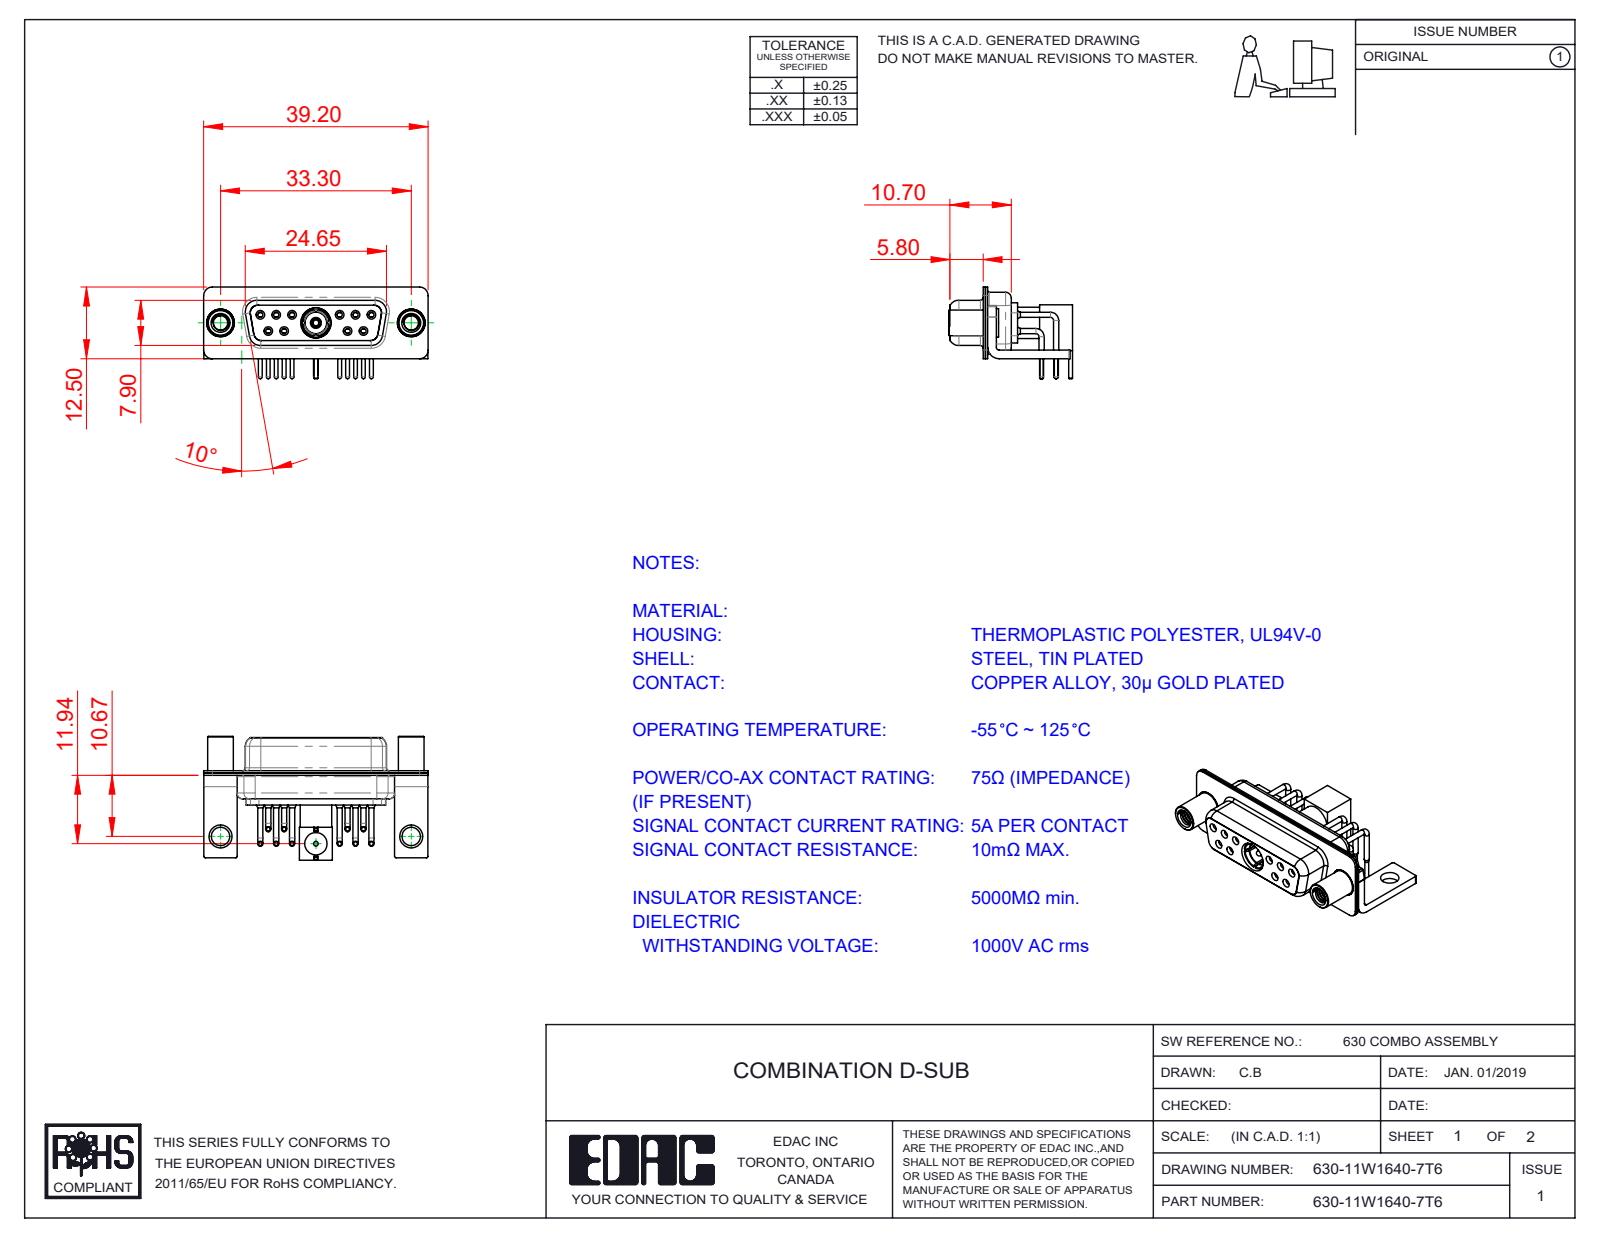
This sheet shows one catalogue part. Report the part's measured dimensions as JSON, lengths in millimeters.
{"part_name": "Co-Ax Plug_RA PC Tail; Locking Collar; 630Combo Shell Rear_15 Contacts; RA Back Shell (+8 more)", "step_written_by": "SolidWorks 2020 (CONFIG_CONTROL_DESIGN)", "units": "millimeters", "bodies": {"solids": 23, "faces": 1075, "planar": 306, "cylindrical": 504, "other": 265}, "overall_size": [39.2, 21.61, 16], "volume_mm3": 3196, "surface_area_mm2": 7818, "round_holes": [[1.1, 11], [1.5, 11], [0.9, 10], [2, 10], [1.7, 6], [1.6, 4], [4.85, 3], [2.5, 2], [3.2, 2], [4, 2], [4.05, 2], [0.8, 1]], "round_bosses_or_shafts": [[0.9, 10], [0.65, 10], [1.6, 6], [5, 3], [4.95, 2], [4.8, 2], [4.5, 2], [5.5, 1]], "partial_cylinders_radius": [[0.25, 16], [1.5, 16], [2, 13], [1.35, 12], [1.6, 8], [0.5, 5], [0.6, 4], [0.65, 4]], "face_to_face_distances": [0.4, 0.8, 1.4, 0.45, 1.8, 8.45, 8.9, 1.5, 6.2, 2.3], "hole_center_spacings": [3.16, 2.77, 13.85, 11.08, 16.62, 5.03, 5.04, 5.54]}
